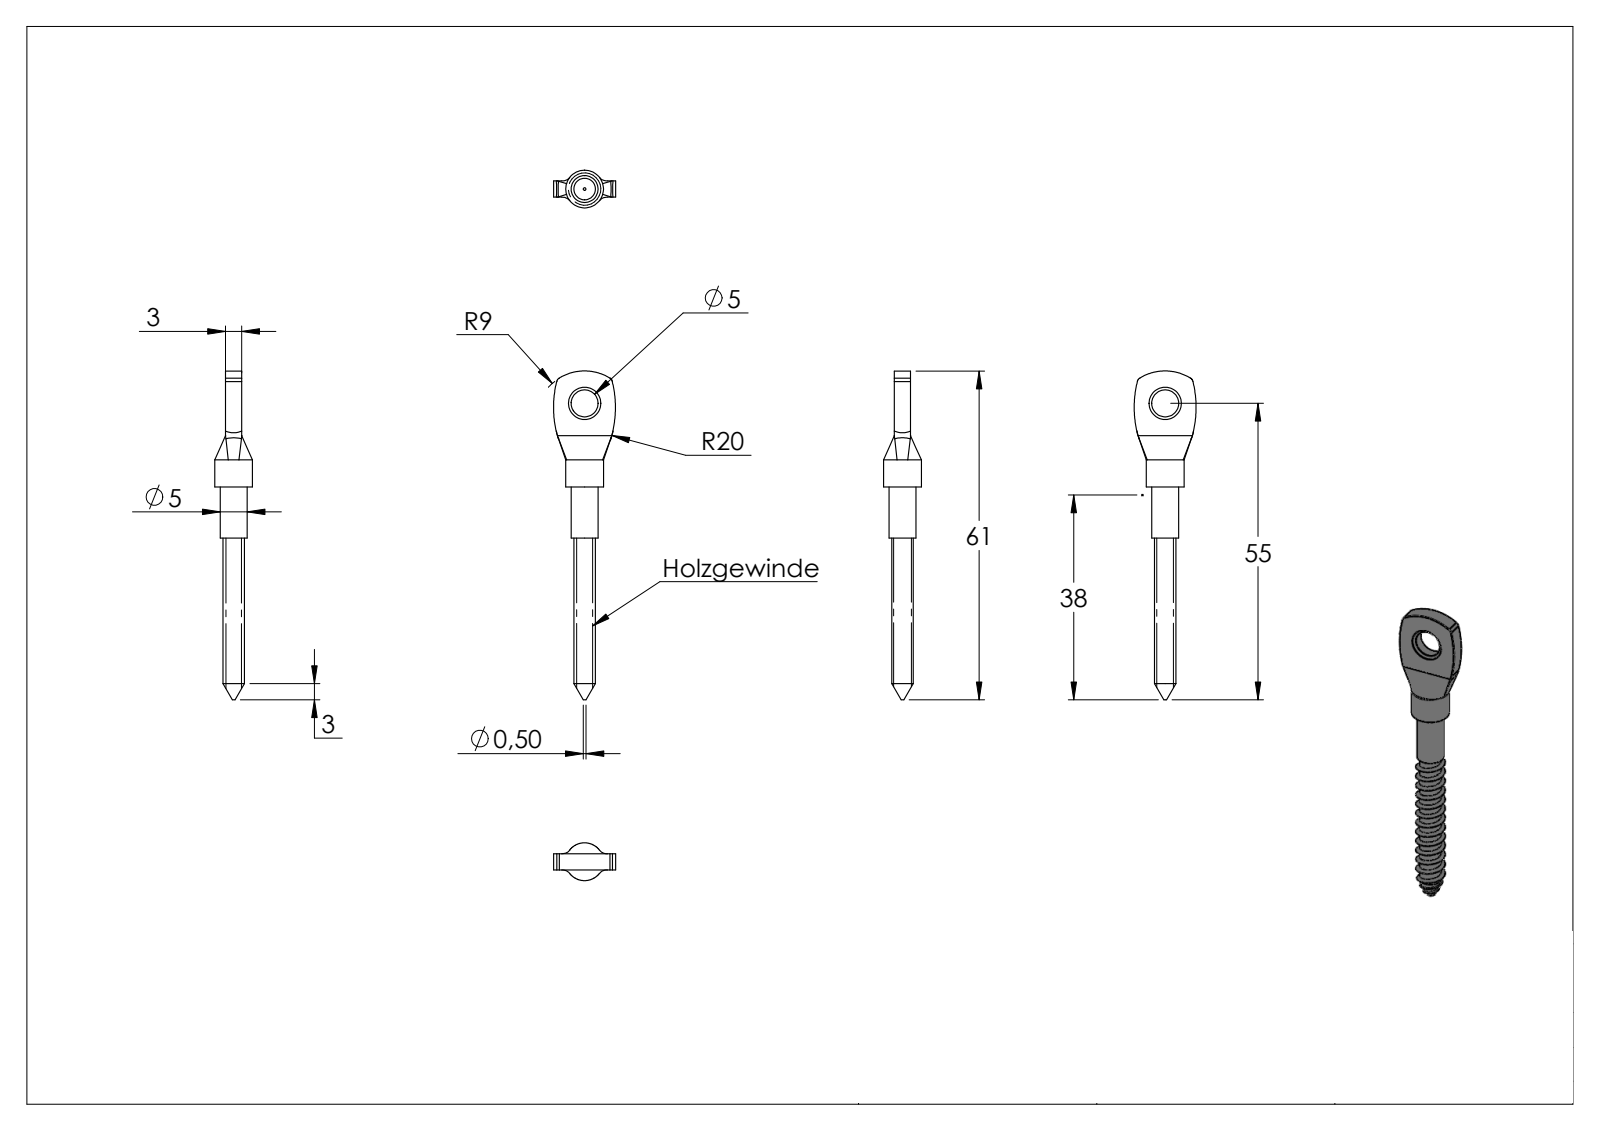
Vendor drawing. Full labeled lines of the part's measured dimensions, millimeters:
Part name (STEP PRODUCT): 100055005
STEP written by: SolidWorks 2015 (CONFIG_CONTROL_DESIGN)
Units: millimetres
Bodies: 1 solid, 260 faces (83 planar, 48 cylindrical, 129 other)
Overall size (bounding box): 61 × 11.5 × 7
Volume: 1 204 mm³ · Surface area: 1 107 mm²
Round holes (diameter × count): ⌀5 ×1
Round bosses / shafts (diameter × count): ⌀7 ×1, ⌀5 ×1, ⌀4 ×1
Partial cylindrical surfaces — rounded edges, fillets, slot ends (radius × count): R1 ×2, R20 ×2, R2.6 ×1, R9 ×1
Main face-to-face distances: 3, 9.5, 30, 39.5, 0.68, 0.62, 0.7, 0.6, 0.37, 0.64
